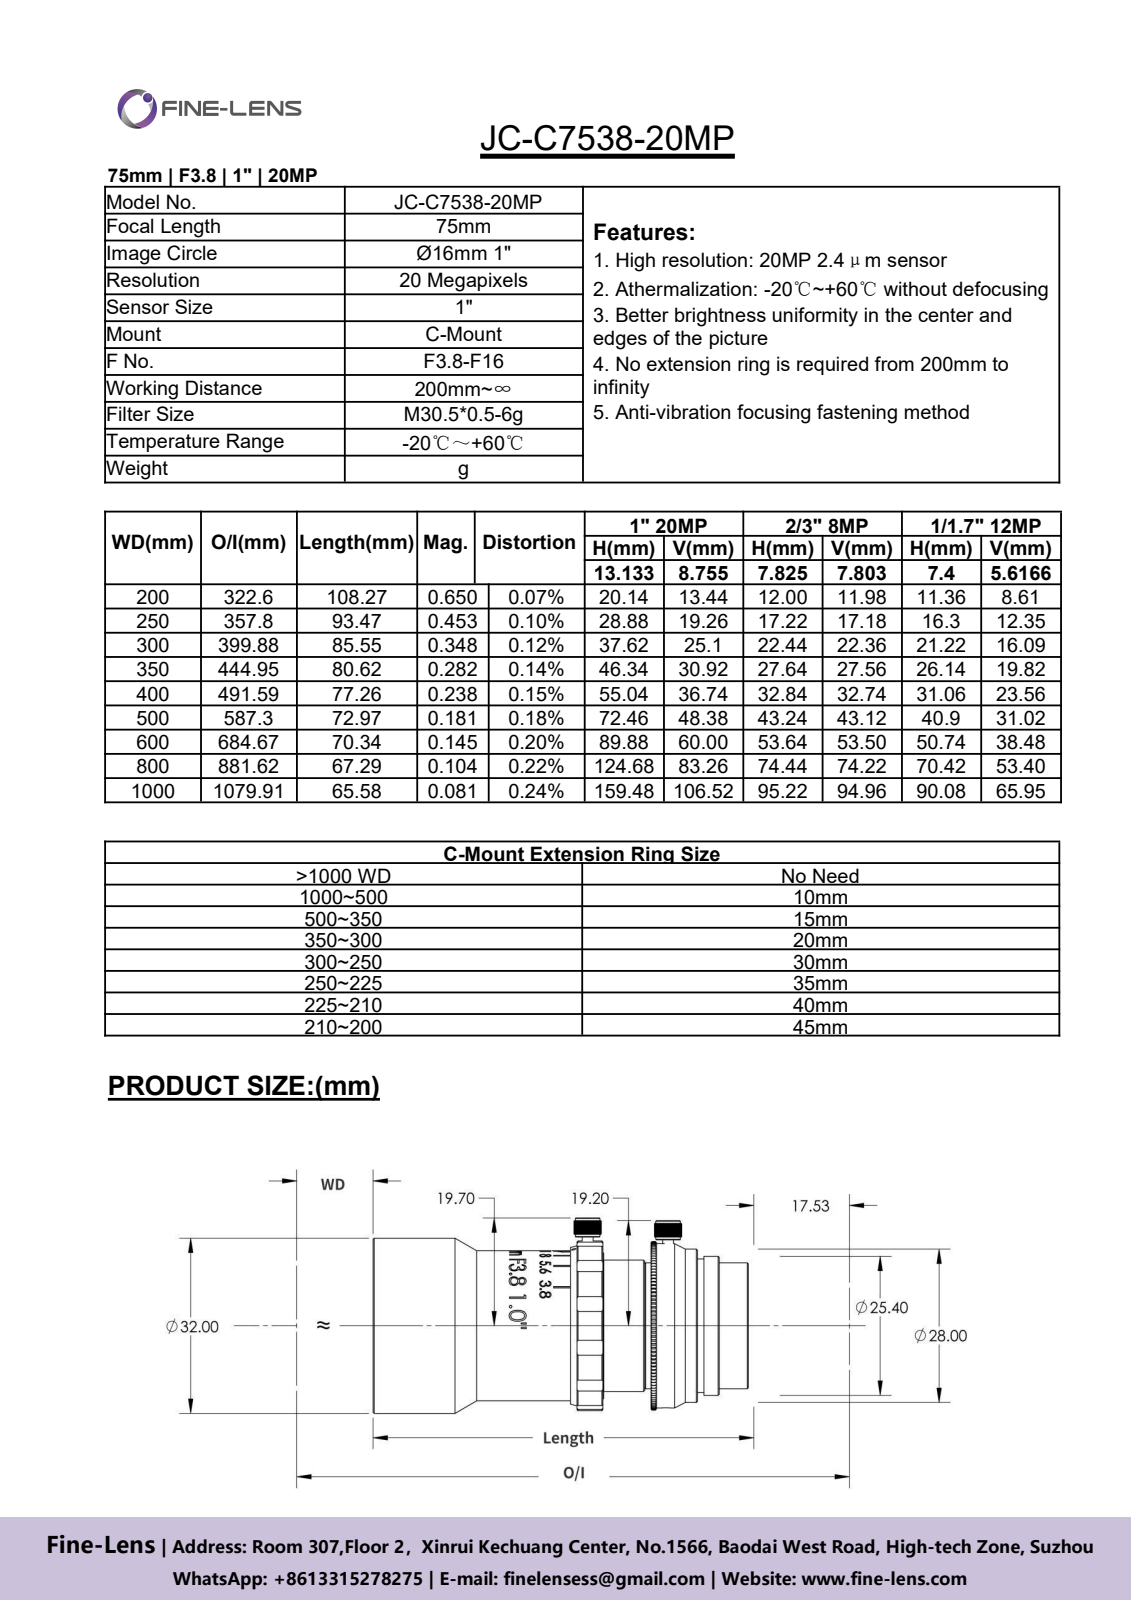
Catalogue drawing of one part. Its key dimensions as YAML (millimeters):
step_written_by: "SolidWorks 2018 (AUTOMOTIVE_DESIGN)"
units: millimeters
bodies: {solids: 5, faces: 2055, planar: 711, cylindrical: 429, other: 915}
overall_size: [65, 35.7, 32]
volume: 38926
surface_area: 12404
round_holes:
  - {diameter: 1.2, count: 5}
  - {diameter: 1.6, count: 2}
  - {diameter: 0.8, count: 1}
  - {diameter: 22.4, count: 1}
  - {diameter: 24.6, count: 1}
  - {diameter: 27.6, count: 1}
  - {diameter: 29, count: 1}
  - {diameter: 30, count: 1}
  - {diameter: 30.7, count: 1}
round_bosses_or_shafts:
  - {diameter: 4.5, count: 2}
  - {diameter: 2, count: 2}
  - {diameter: 32, count: 1}
  - {diameter: 28, count: 1}
  - {diameter: 27.4, count: 1}
  - {diameter: 25.4, count: 1}
  - {diameter: 24.4, count: 1}
  - {diameter: 24, count: 1}
partial_cylinders:
  - {radius: 2.5, count: 14}
  - {radius: 1, count: 1}
  - {radius: 13.6, count: 1}
  - {radius: 15.4, count: 1}
  - {radius: 15.5, count: 1}
face_to_face_distances: [62, 43.02, 18.98, 4.9, 33.87, 9.15, 28.13, 38.12, 4.25, 23.88]
hole_center_spacings: [7.97, 9.38, 15.16, 9.37, 15.17, 7.98, 9.5]
